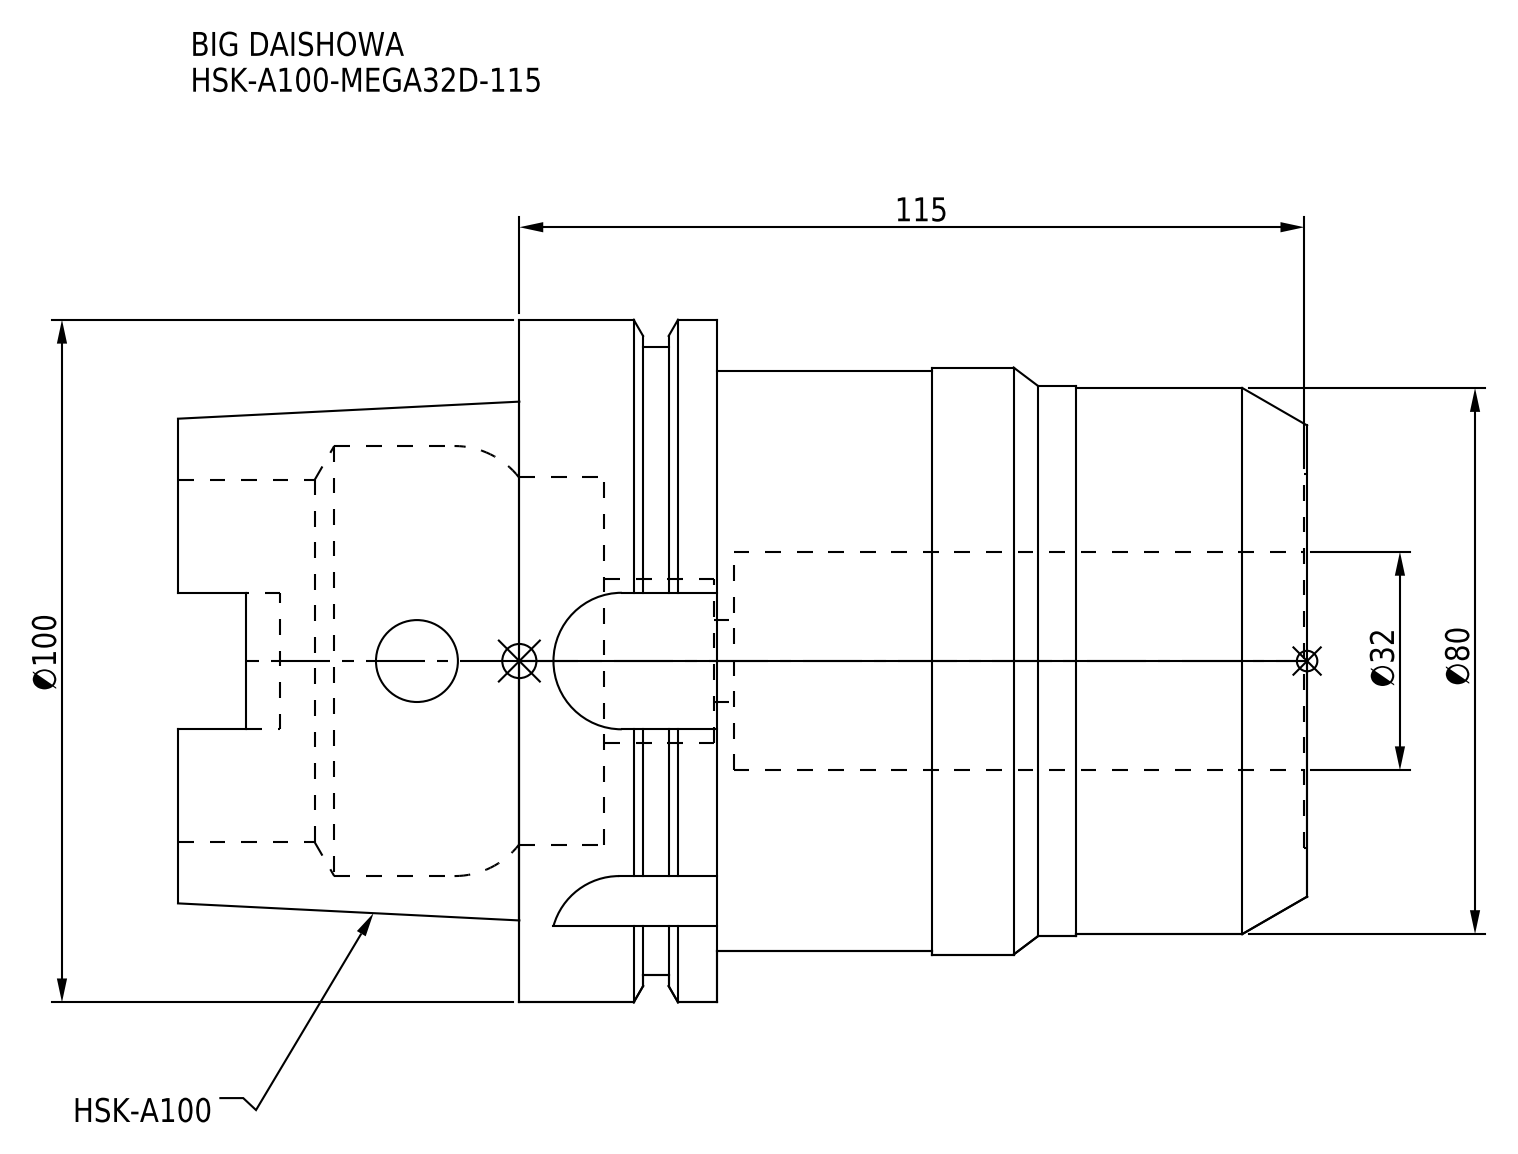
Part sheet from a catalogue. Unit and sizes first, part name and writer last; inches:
Units: inches
Overall size (bounding box): 6.512 × 3.937 × 3.937
Round holes (diameter × count): ⌀0.472 ×2, ⌀0.945 ×1, ⌀1.26 ×1, ⌀2.087 ×1, ⌀2.118 ×1, ⌀2.154 ×1, ⌀2.48 ×1
Round bosses / shafts (diameter × count): ⌀3.937 ×1, ⌀3.622 ×1, ⌀3.386 ×1, ⌀3.346 ×1, ⌀3.177 ×1, ⌀3.15 ×1
Partial cylindrical surfaces — rounded edges, fillets, slot ends (radius × count): R0.192 ×4, R0.394 ×4
Main face-to-face distances: 1.142, 0.652, 0.49, 3.386, 4.037, 4.528, 0.016, 3.402, 4.053, 4.543
Volume: 39.35 in³ · Surface area: 123.3 in²
Bodies: 1 solid, 98 faces (36 planar, 44 cylindrical, 18 other)
Part name (STEP PRODUCT): HSK-A100-MEGA32D-115
STEP written by: CREO PARAMETRIC BY PTC INC, 2016380 (AUTOMOTIVE_DESIGN)
